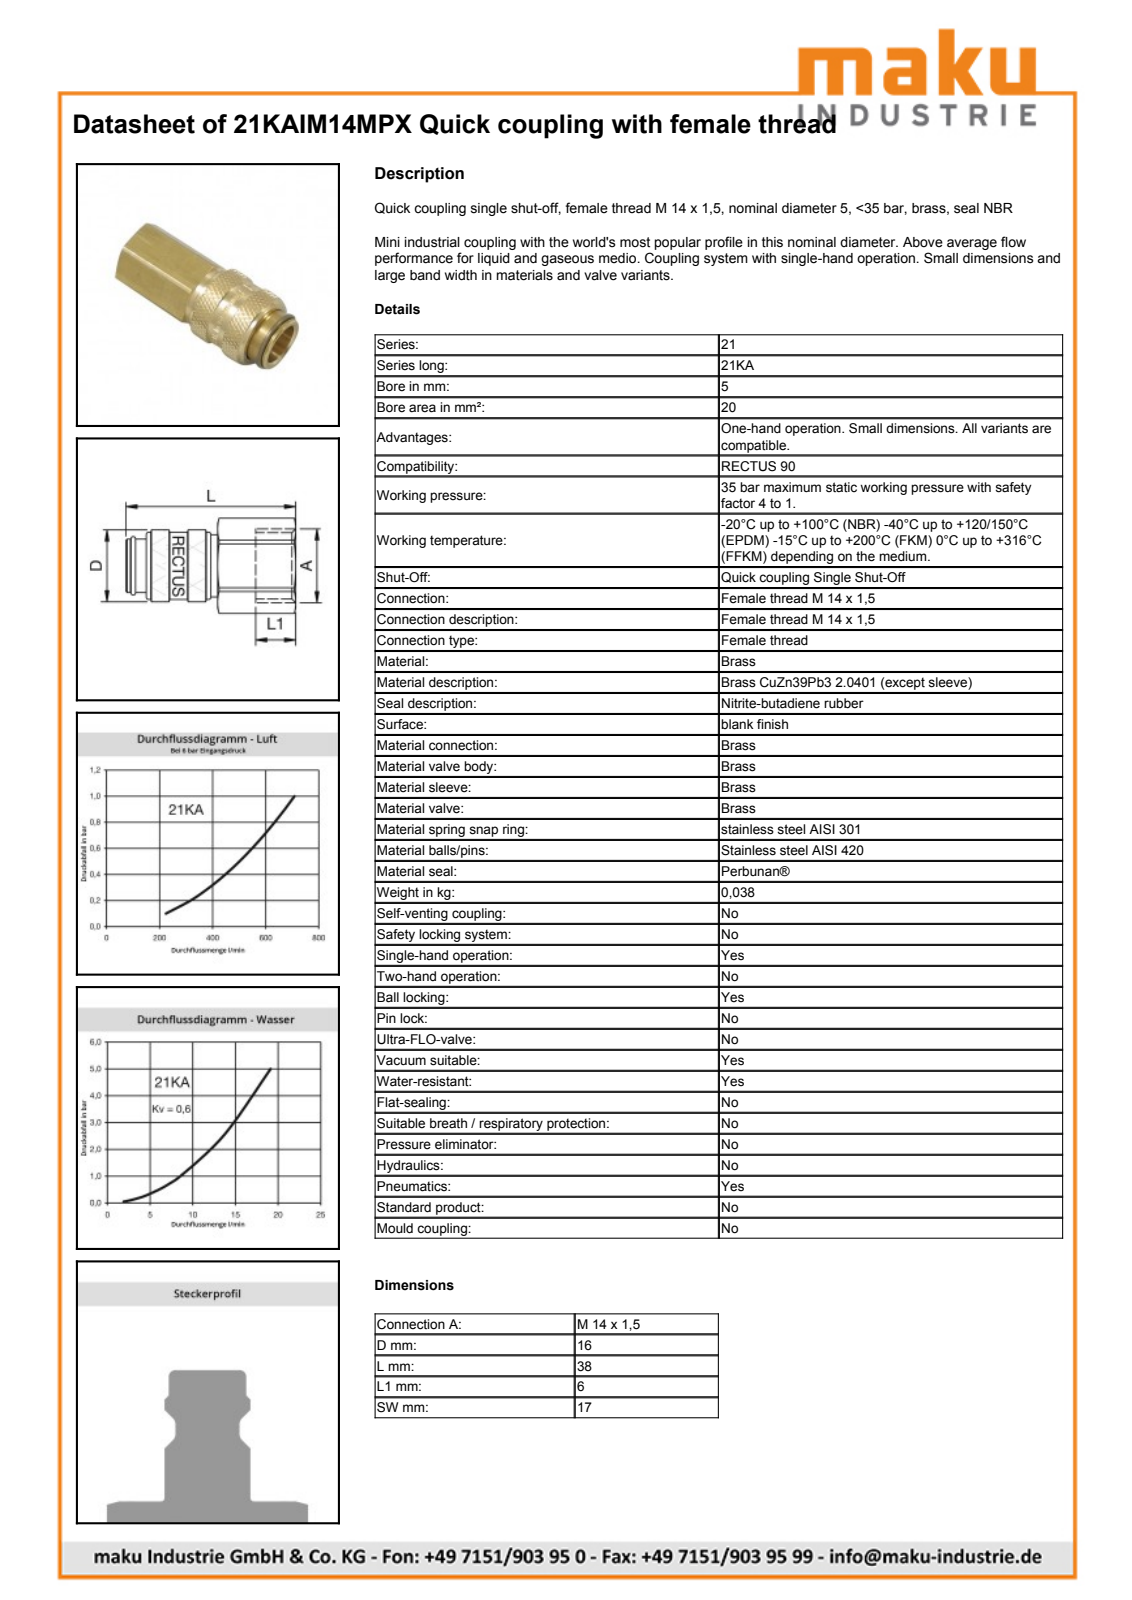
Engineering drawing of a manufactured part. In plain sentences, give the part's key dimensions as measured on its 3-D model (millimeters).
The part is named "D110516". Its 3-D file was written by "Autodesk Inventor 2013 (AUTOMOTIVE_DESIGN)". It is 2 solids with 459 faces: 151 planar, 62 cylindrical and 246 other. Overall it measures 38.15 by 19.06 by 18.07 millimeters. Its volume is 6 489 cubic millimeters and its surface area 4 254 square millimeters. Round holes: 1 of diameter 7.5, 1 of diameter 10.7, 1 of diameter 12.15, 1 of diameter 12.5, 1 of diameter 14. Round bosses or shafts: 1 of diameter 16.15, 1 of diameter 15.1, 1 of diameter 12, 1 of diameter 11.15, 1 of diameter 10.22. Partial cylindrical surfaces (rounded edges, fillets, slot ends): 1 of radius 7.45, 1 of radius 9.57. The main face-to-face distances are 17, 29.15, 38.15, 9, 20.6, 8.55, 17.55, 16.15, 4.45, 13.
